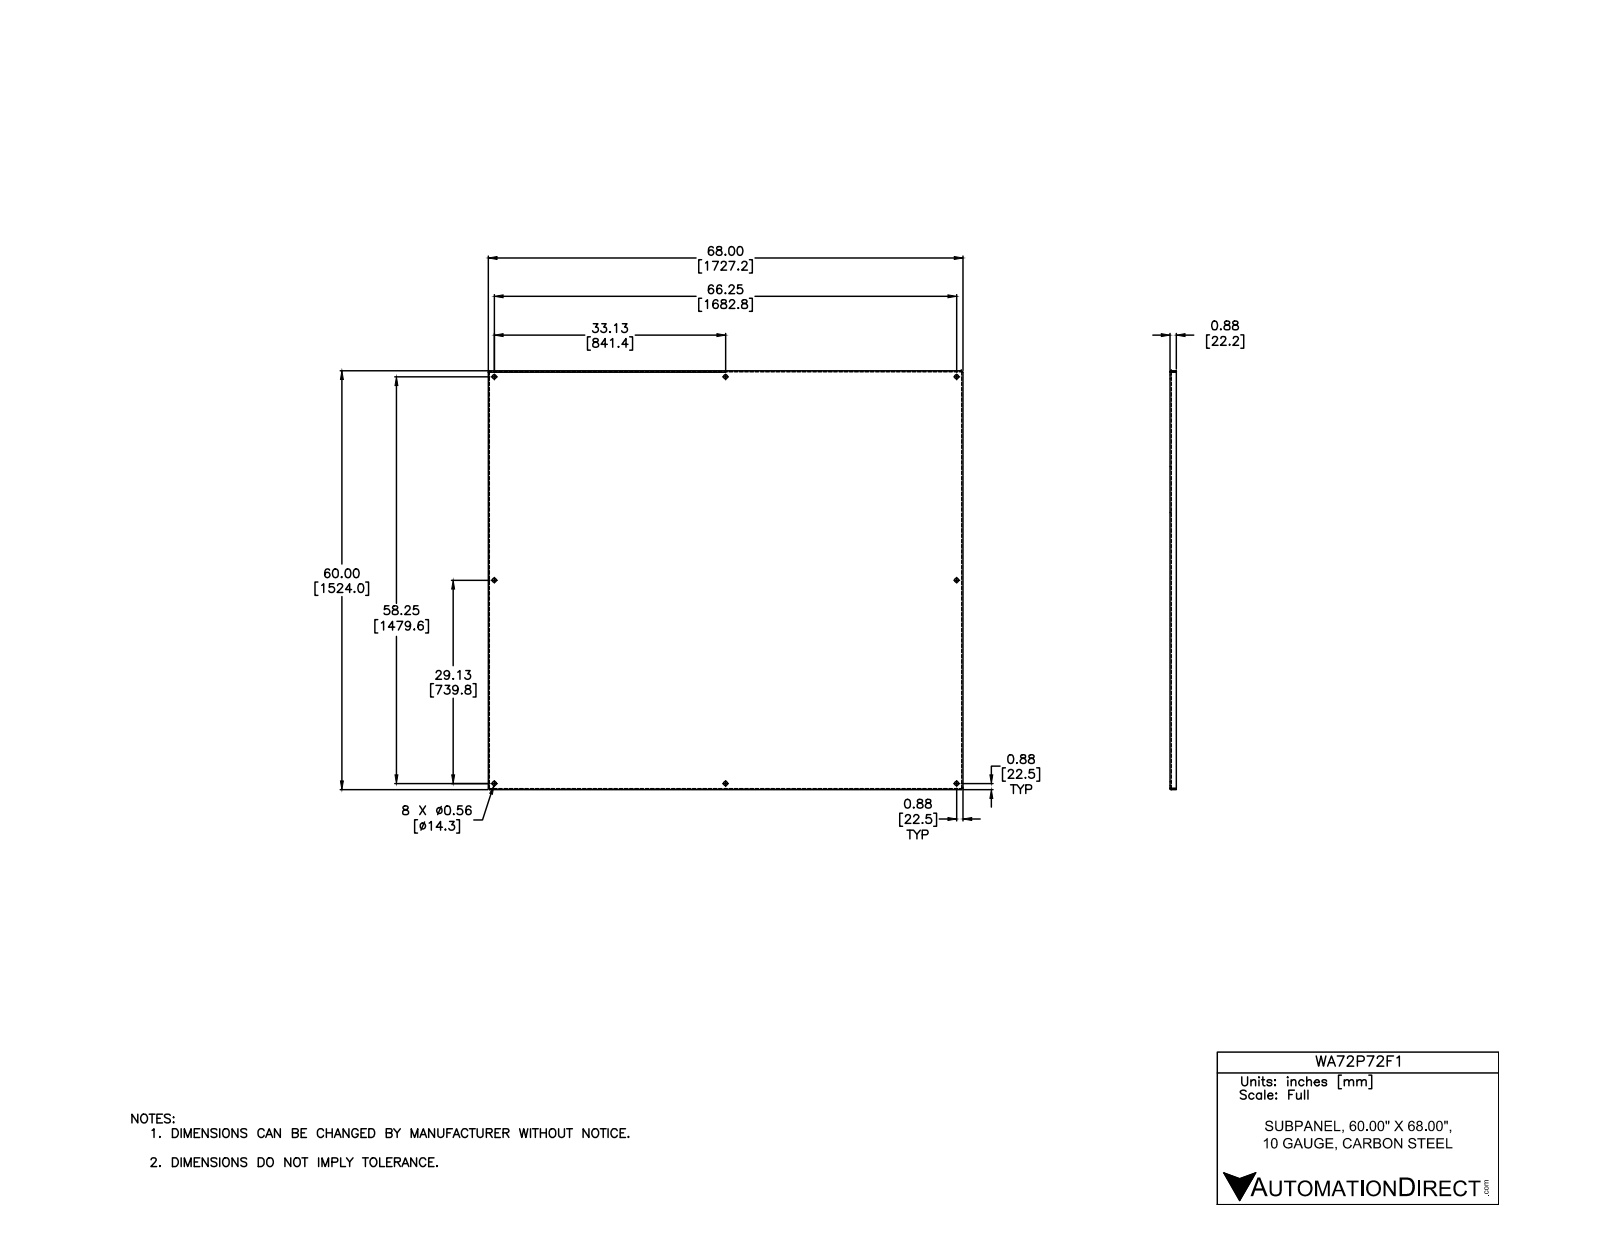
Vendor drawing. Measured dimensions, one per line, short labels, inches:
name: WA_P_F
written by: Autodesk Inventor 2012 (AUTOMOTIVE_DESIGN)
unit: in
bodies: 1 solid, 46 faces (22 planar, 16 cylindrical, 8 other)
size: 68 × 60 × 0.875
volume: 532.3 in³; area: 8 551 in²
holes: 8× ⌀0.563
rounds: 4× R0.031, 4× R0.156
face distances: 0.125, 0.125, 59.875, 60, 59.75, 59.875, 67.875, 67.75, 68, 67.875
hole spacings: 29.125, 44.108, 58.25, 33.125, 33.125, 66.25, 67.009, 67.01
